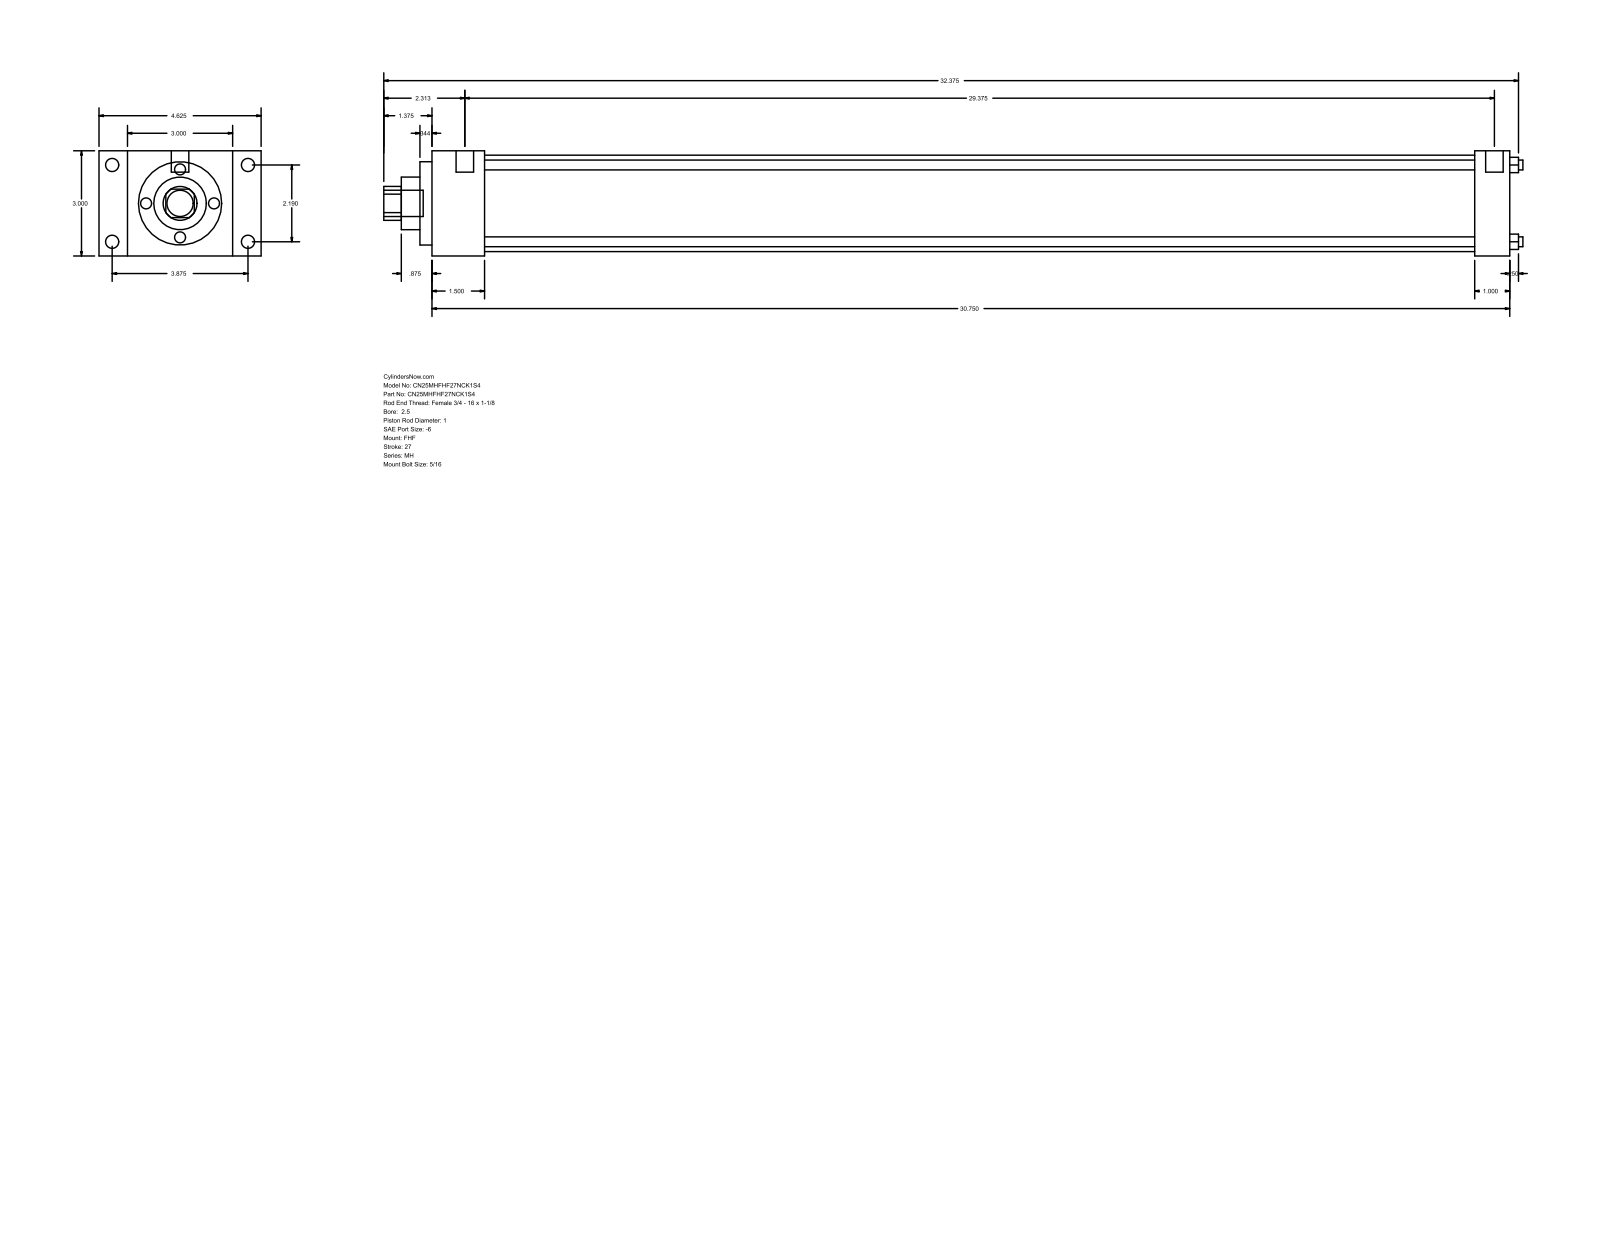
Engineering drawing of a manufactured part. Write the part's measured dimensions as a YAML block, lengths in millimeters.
part_name: "MH_FHF__0250_1"
step_written_by: "GSSL Pune (CONFIG_CONTROL_DESIGN)"
units: millimeters
bodies: {solids: 0, faces: 90, planar: 61, cylindrical: 29, other: 0}
overall_size: [825.5, 117.47, 76.2]
round_holes:
  - {diameter: 7.14, count: 4}
  - {diameter: 25.4, count: 1}
  - {diameter: 38.1, count: 1}
  - {diameter: 60.33, count: 1}
  - {diameter: 69.85, count: 1}
round_bosses_or_shafts:
  - {diameter: 9.53, count: 4}
  - {diameter: 5.56, count: 4}
  - {diameter: 12.7, count: 2}
  - {diameter: 19.05, count: 1}
partial_cylinders:
  - {radius: 12.29, count: 1}
face_to_face_distances: [76.2, 781.06, 38.11, 742.95, 20.64, 96.84, 117.48, 755.66, 717.55, 25.4]
hole_center_spacings: [39.33, 55.62, 78.66]
